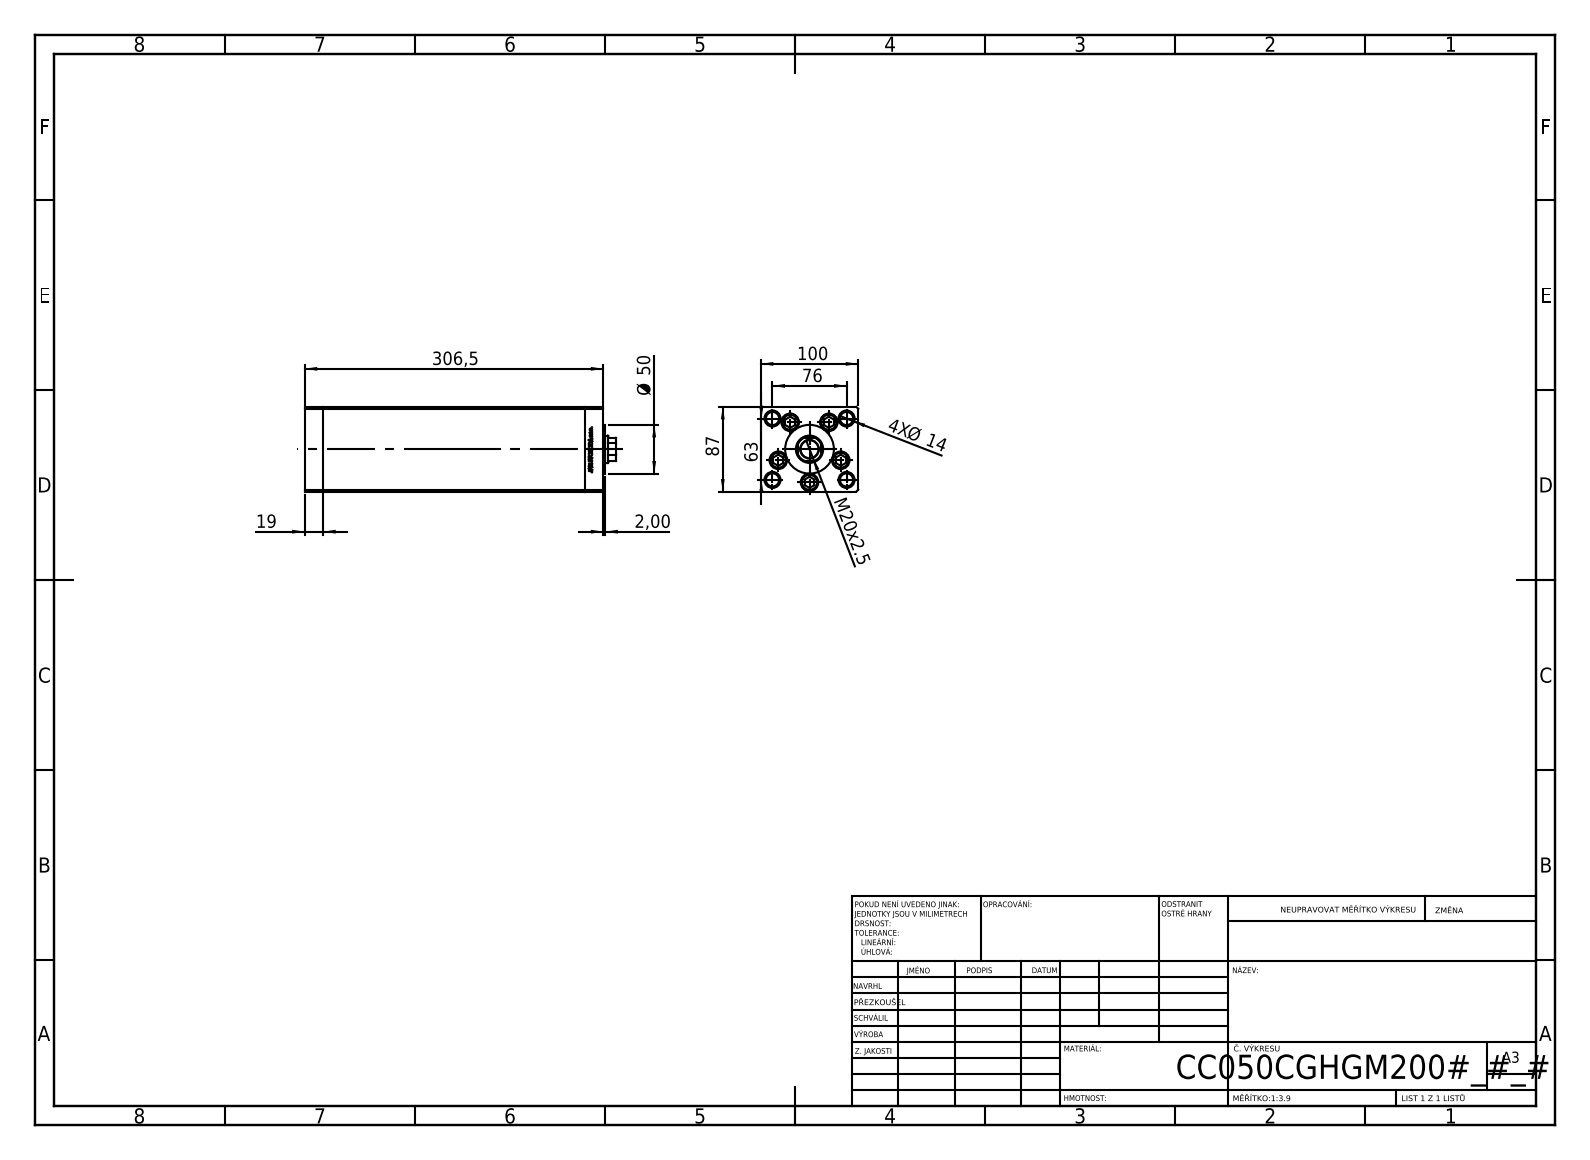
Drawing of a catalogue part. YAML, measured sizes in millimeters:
part_name: "ALLEN BOLT; V220C FRONT; V220C_C MIDDLE; V220C_VC_C (+1 more)"
step_written_by: "SolidWorks 2019 (CONFIG_CONTROL_DESIGN)"
units: millimeters
bodies: {solids: 13, faces: 1186, planar: 548, cylindrical: 176, other: 462}
overall_size: [319.5, 100, 87]
volume: 2177000
surface_area: 311406
round_holes:
  - {diameter: 13.5, count: 9}
  - {diameter: 18, count: 5}
  - {diameter: 2, count: 4}
  - {diameter: 12, count: 4}
  - {diameter: 13.16, count: 4}
  - {diameter: 16.5, count: 4}
  - {diameter: 17, count: 1}
  - {diameter: 18.5, count: 1}
  - {diameter: 28, count: 1}
round_bosses_or_shafts:
  - {diameter: 8, count: 5}
  - {diameter: 17, count: 4}
  - {diameter: 50, count: 1}
partial_cylinders:
  - {radius: 0.93, count: 2}
  - {radius: 13.5, count: 1}
face_to_face_distances: [100, 87, 19, 268.5, 287.5, 34.25, 306.5, 272.25, 253.25, 15.25]
hole_center_spacings: [34, 49.36, 18.59, 21.03, 38.08, 39.27, 40.83, 43.24]
